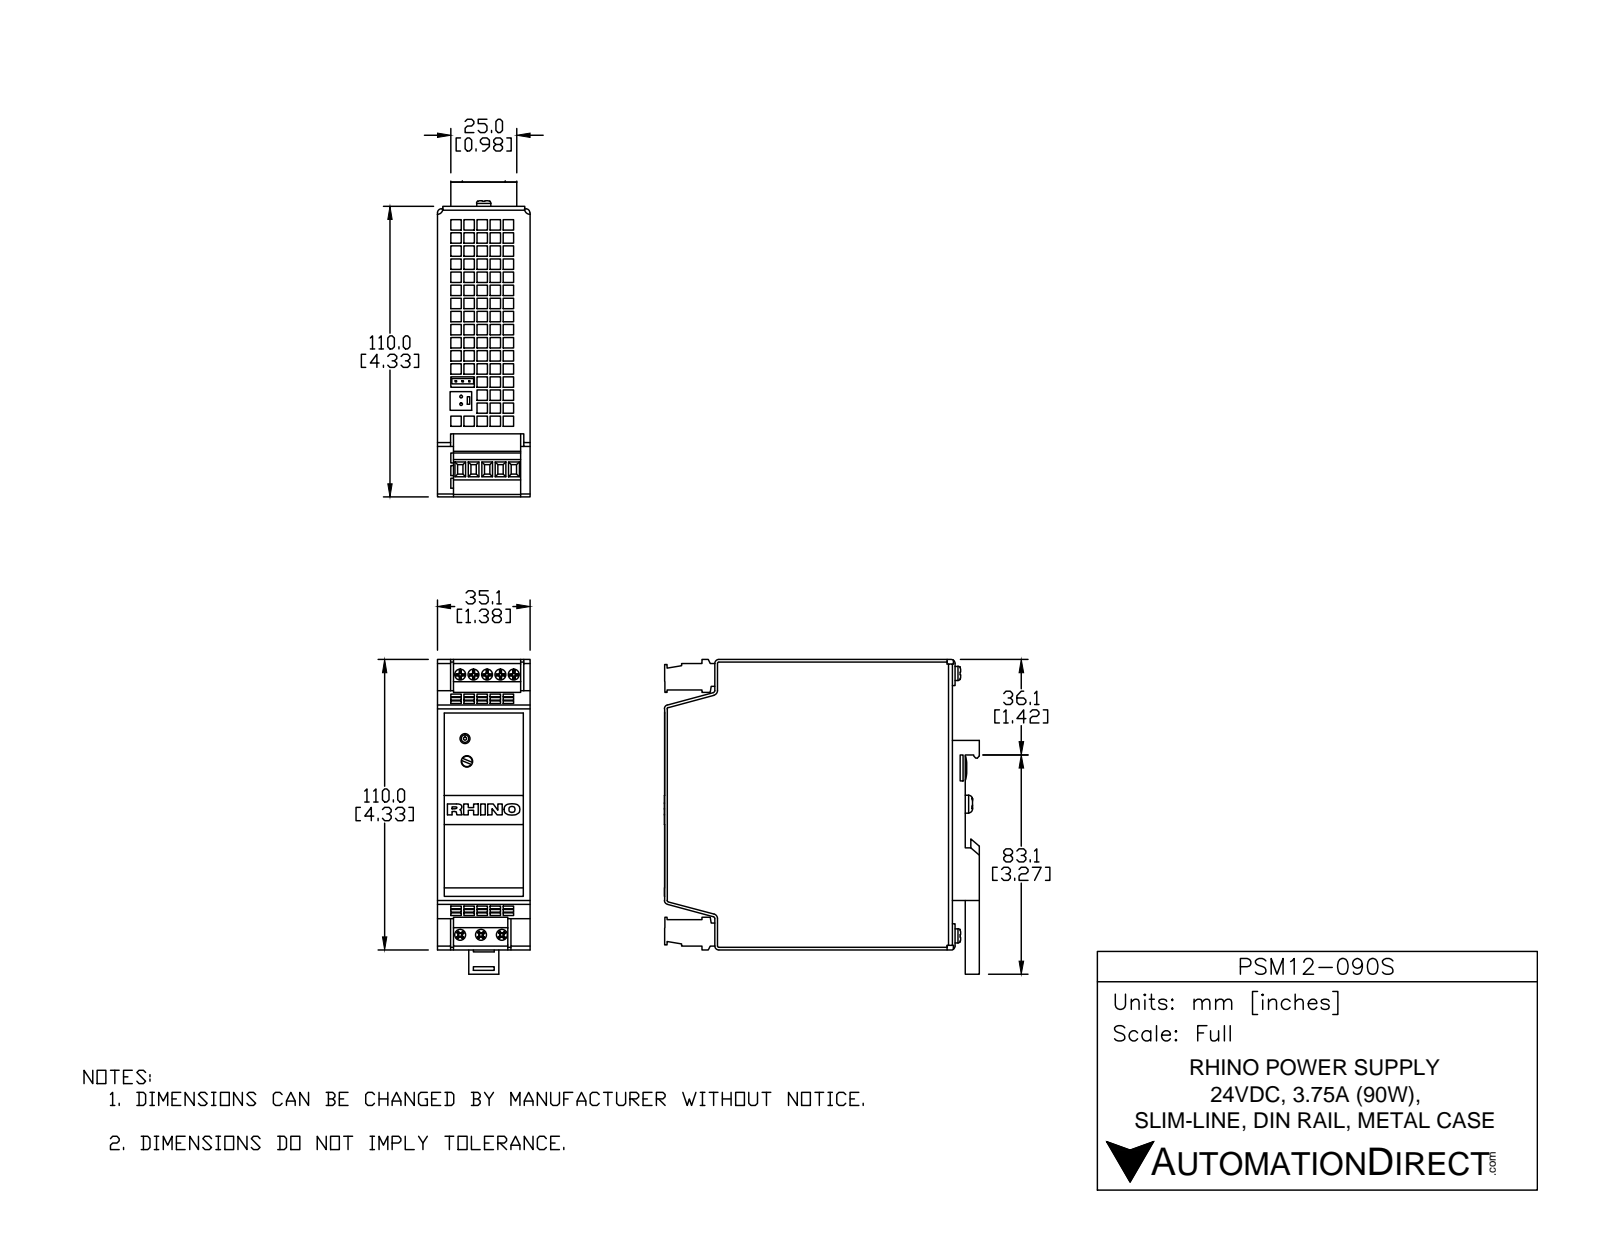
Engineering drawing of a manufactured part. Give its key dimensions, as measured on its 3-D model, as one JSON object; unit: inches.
{"part_name": "PSM24-090S", "step_written_by": "SolidWorks 2011 (CONFIG_CONTROL_DESIGN)", "units": "inches", "bodies": {"solids": 1, "faces": 1512, "planar": 1389, "cylindrical": 60, "other": 63}, "overall_size": [4.692, 4.691, 1.38], "volume_in3": 25.36, "surface_area_in2": 77.69, "round_holes": [[0.16, 8], [0.15, 1], [0.172, 1]], "round_bosses_or_shafts": [[0.21, 2], [0.265, 1], [0.109, 1], [0.041, 1], [0.041, 1]], "partial_cylinders_radius": [[0.06, 8], [0.02, 4], [0.03, 2], [0.07, 2], [0.081, 2]], "face_to_face_distances": [1.378, 0.04, 4.29, 4.33, 4.291, 4.25, 0.04, 0.196, 1.181, 0.4], "hole_center_spacings": [0.2, 0.4, 0.6, 1.298, 3.88, 0.31, 0.31, 0.341]}
